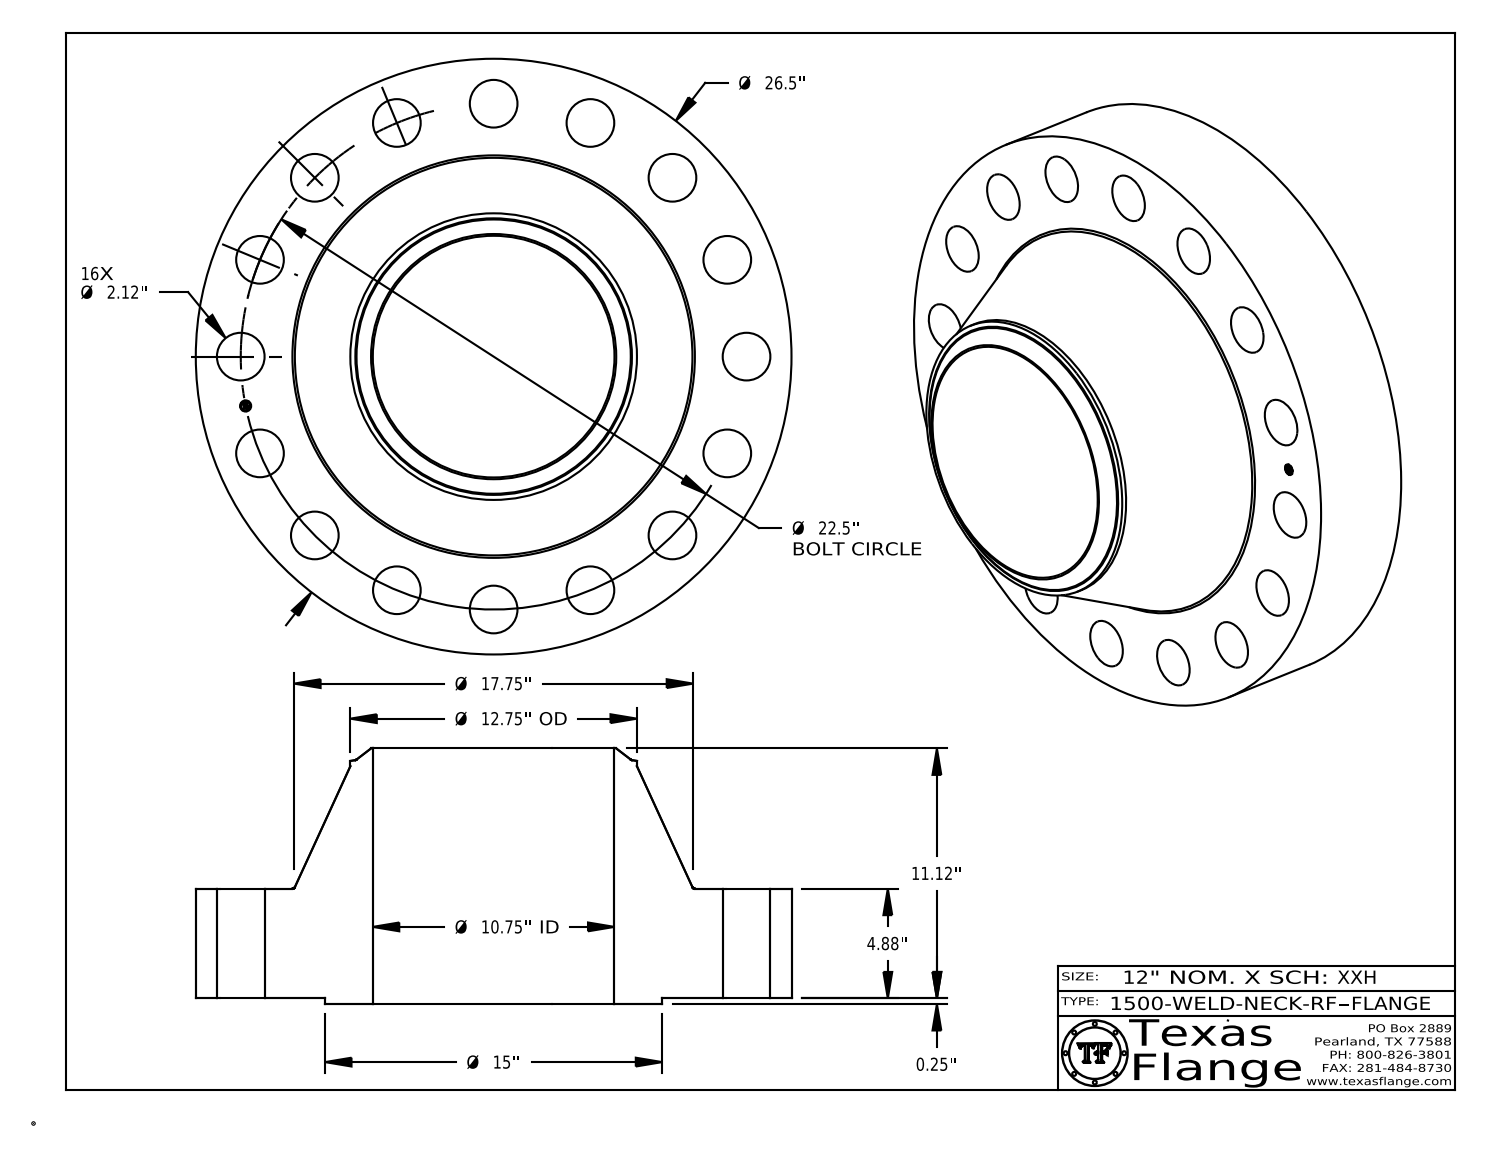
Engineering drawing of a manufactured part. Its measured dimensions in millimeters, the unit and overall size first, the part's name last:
Units: millimetres
Overall size (bounding box): 673.1 × 673.1 × 288.8
Round holes (diameter × count): ⌀53.8 ×16, ⌀12.6 ×1, ⌀273.1 ×1
Round bosses / shafts (diameter × count): ⌀0.8 ×8, ⌀673.1 ×1, ⌀381 ×1, ⌀323.9 ×1, ⌀9.9 ×1
Main face-to-face distances: 124, 6.4, 130.3, 288.8, 282.4, 158.5, 129.9, 123.6, 0.4, 158.9
Hole centre spacings: 317.5, 528, 560.5, 285.8, 218.7, 404.1, 111.5, 111.5
Volume: 41 330 000 mm³ · Surface area: 1 492 000 mm²
Bodies: 1 solid, 439 faces (369 planar, 60 cylindrical, 10 other)
Part name (STEP PRODUCT): 1500-WELD-NECK-RF
STEP written by: CATIA V5 STEP AP214 (AUTOMOTIVE_DESIGN)
